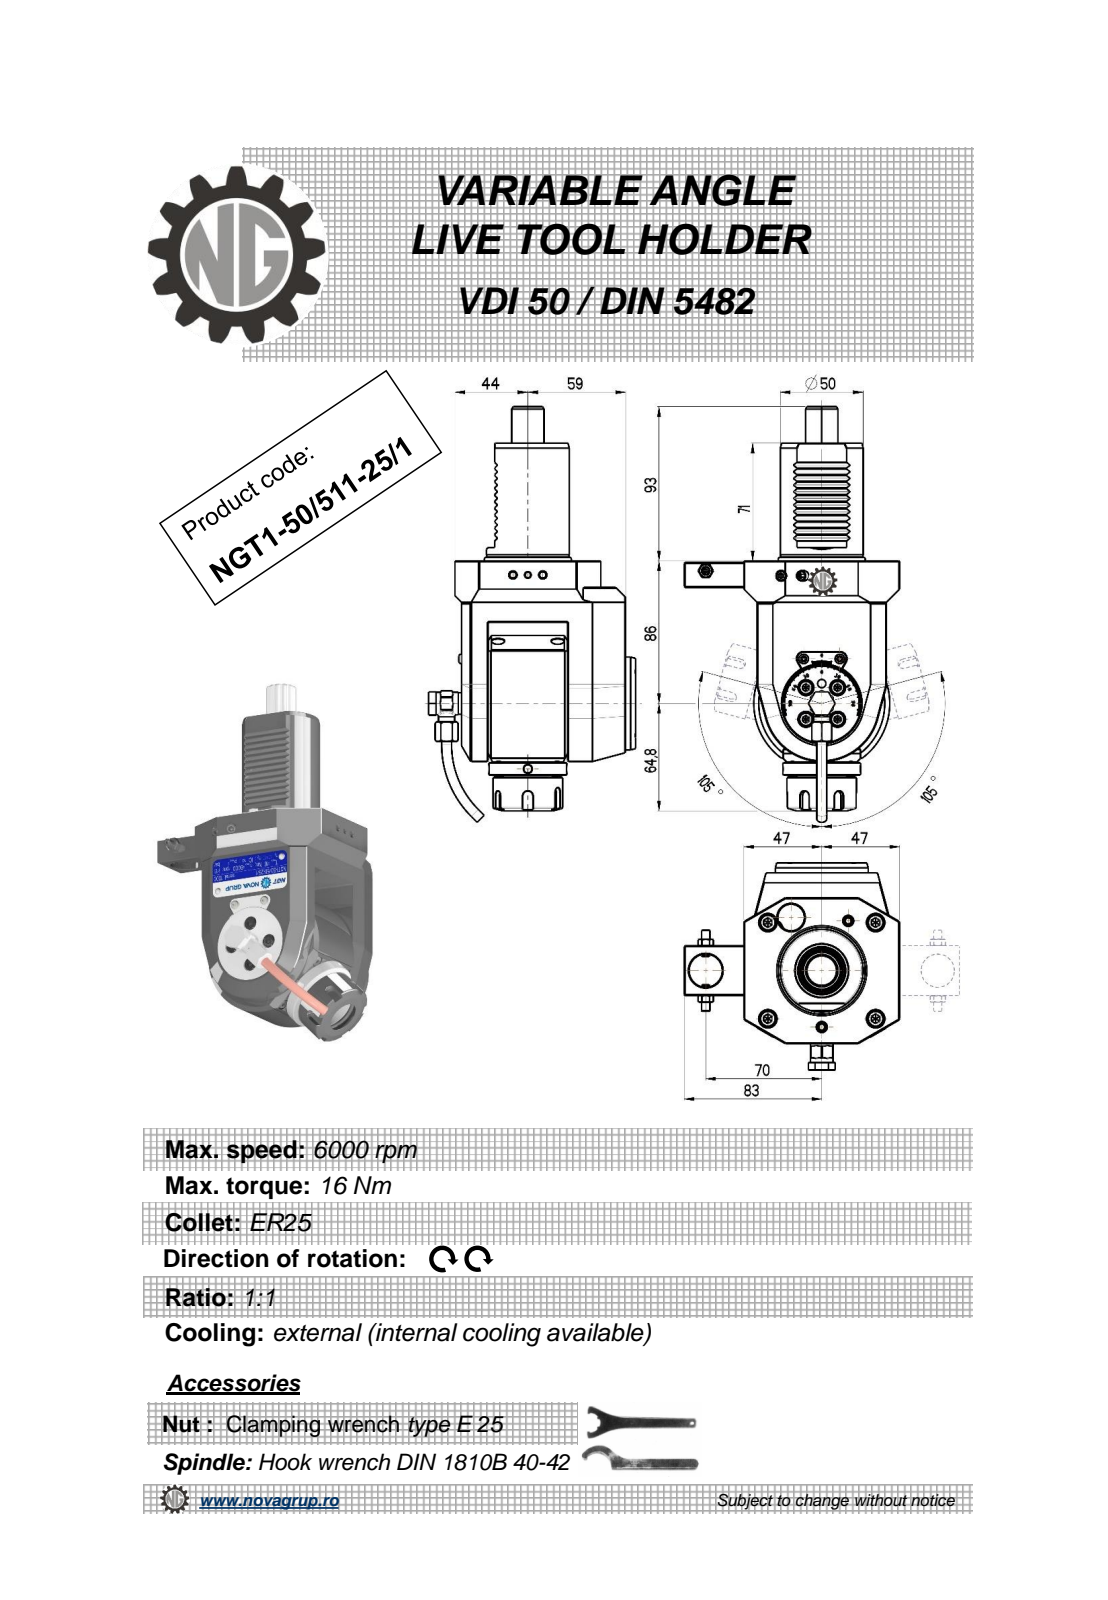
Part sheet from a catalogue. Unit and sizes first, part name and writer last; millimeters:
Units: millimetres
Overall size (bounding box): 250.67 × 130 × 124.9
Round holes (diameter × count): ⌀4 ×3, ⌀5 ×2, ⌀3 ×1, ⌀6.2 ×1, ⌀9 ×1, ⌀9.5 ×1, ⌀10 ×1, ⌀11 ×1, ⌀20 ×1, ⌀20.3 ×1
Round bosses / shafts (diameter × count): ⌀6 ×2, ⌀5.7 ×2, ⌀82 ×1, ⌀56 ×1, ⌀50 ×1, ⌀47 ×1, ⌀42 ×1, ⌀35 ×1
Partial cylindrical surfaces — rounded edges, fillets, slot ends (radius × count): R3.33 ×24, R0.26 ×12, R0.3 ×12, R0.16 ×6, R3 ×5, R0.5 ×4, R1 ×2, R10 ×2
Main face-to-face distances: 37, 16, 99, 8, 6, 21, 64, 105, 20, 35
Hole centre spacings: 0.4, 39.45, 49, 49.4, 70, 85.45, 85.68, 116.95
Volume: 1 013 000 mm³ · Surface area: 91 578 mm²
Bodies: 1 solid, 659 faces (261 planar, 184 cylindrical, 214 other)
Part name (STEP PRODUCT): NGT1_50_511_25_1
STEP written by: PRO/ENGINEER BY PARAMETRIC TECHNOLOGY CORPORATION, 2010280 (CONFIG_CONTROL_DESIGN)
